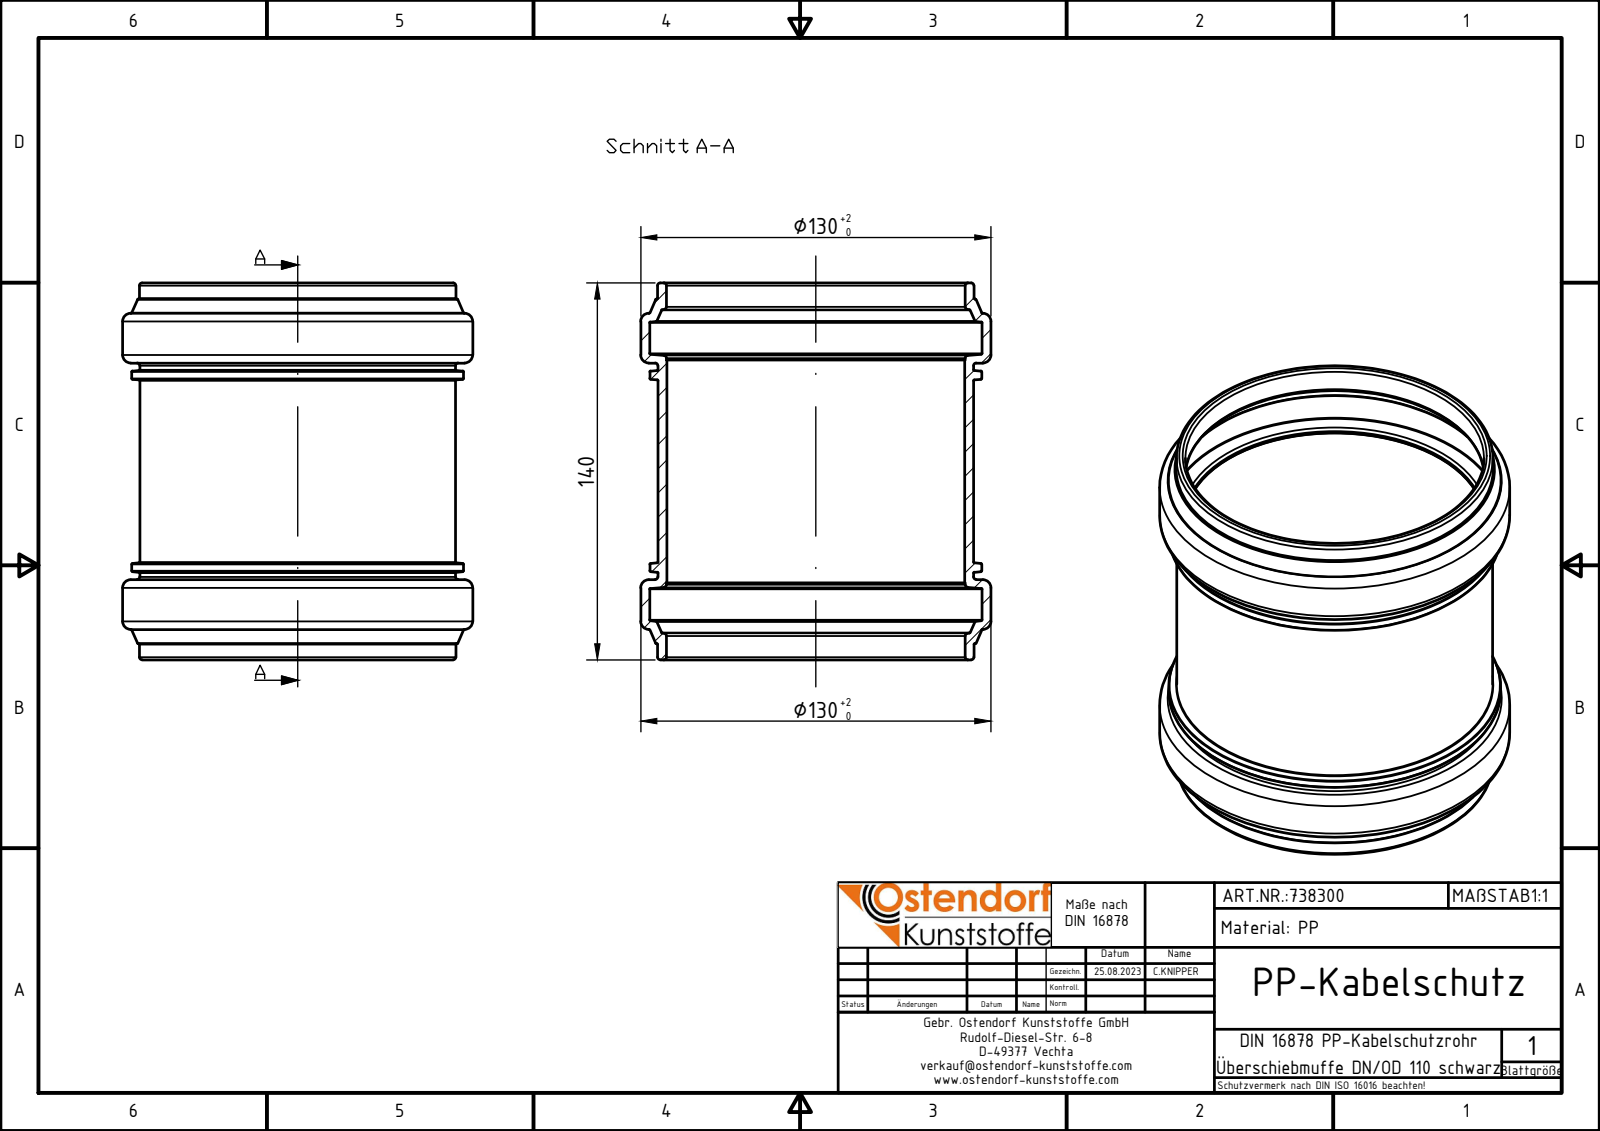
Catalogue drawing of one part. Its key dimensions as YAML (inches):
part_name: "738300z"
step_written_by: "Autodesk Inventor 2024 (AUTOMOTIVE_DESIGN)"
units: inches
bodies: {solids: 1, faces: 76, planar: 10, cylindrical: 16, other: 50}
overall_size: [5.512, 5.118, 5.118]
volume: 12.27
surface_area: 188.1
round_holes:
  - {diameter: 4.354, count: 1}
  - {diameter: 4.366, count: 1}
  - {diameter: 4.858, count: 1}
round_bosses_or_shafts:
  - {diameter: 5.118, count: 1}
  - {diameter: 4.85, count: 1}
  - {diameter: 4.626, count: 1}
  - {diameter: 4.614, count: 1}
face_to_face_distances: [1.173, 4.339, 3.165, 5.512, 1.128, 4.384, 0.046, 3.211, 0.238, 5.274]
